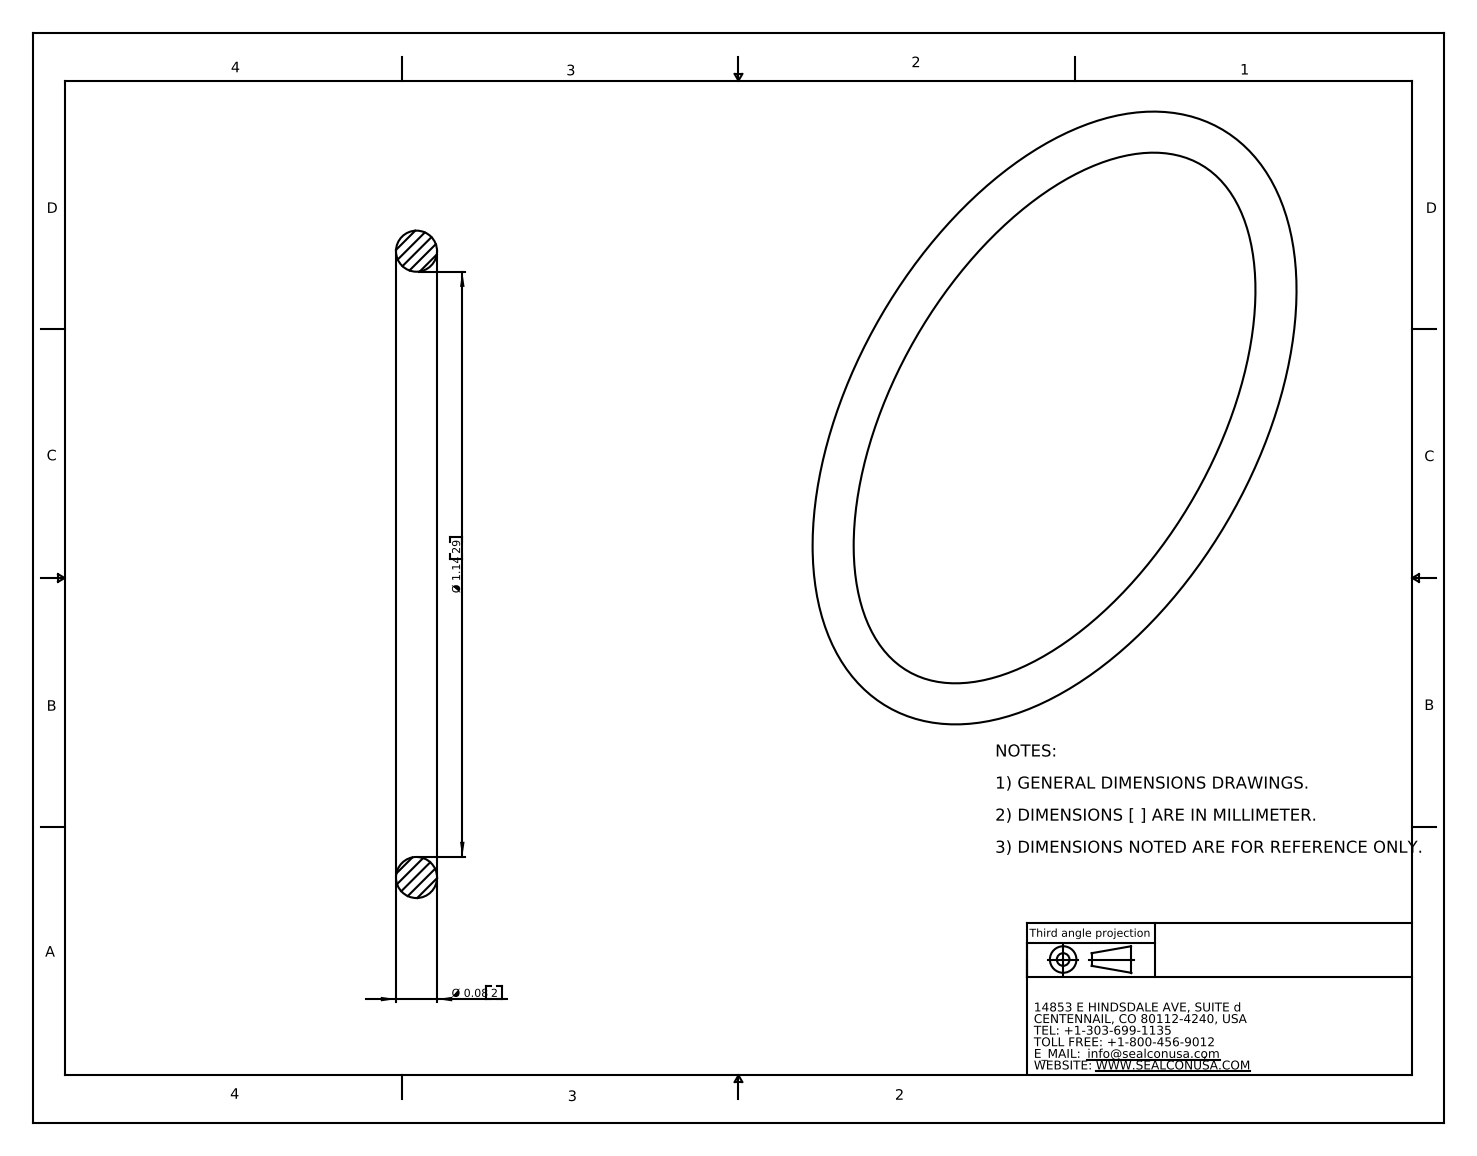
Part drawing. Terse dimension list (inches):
name: OM-32-BN
written by: SolidWorks 2007 (CONFIG_CONTROL_DESIGN)
unit: in
bodies: 1 solid, 4 faces (0 planar, 0 cylindrical, 4 other)
size: 1.3 × 1.3 × 0.08
volume: 0.019 in³; area: 0.963 in²
